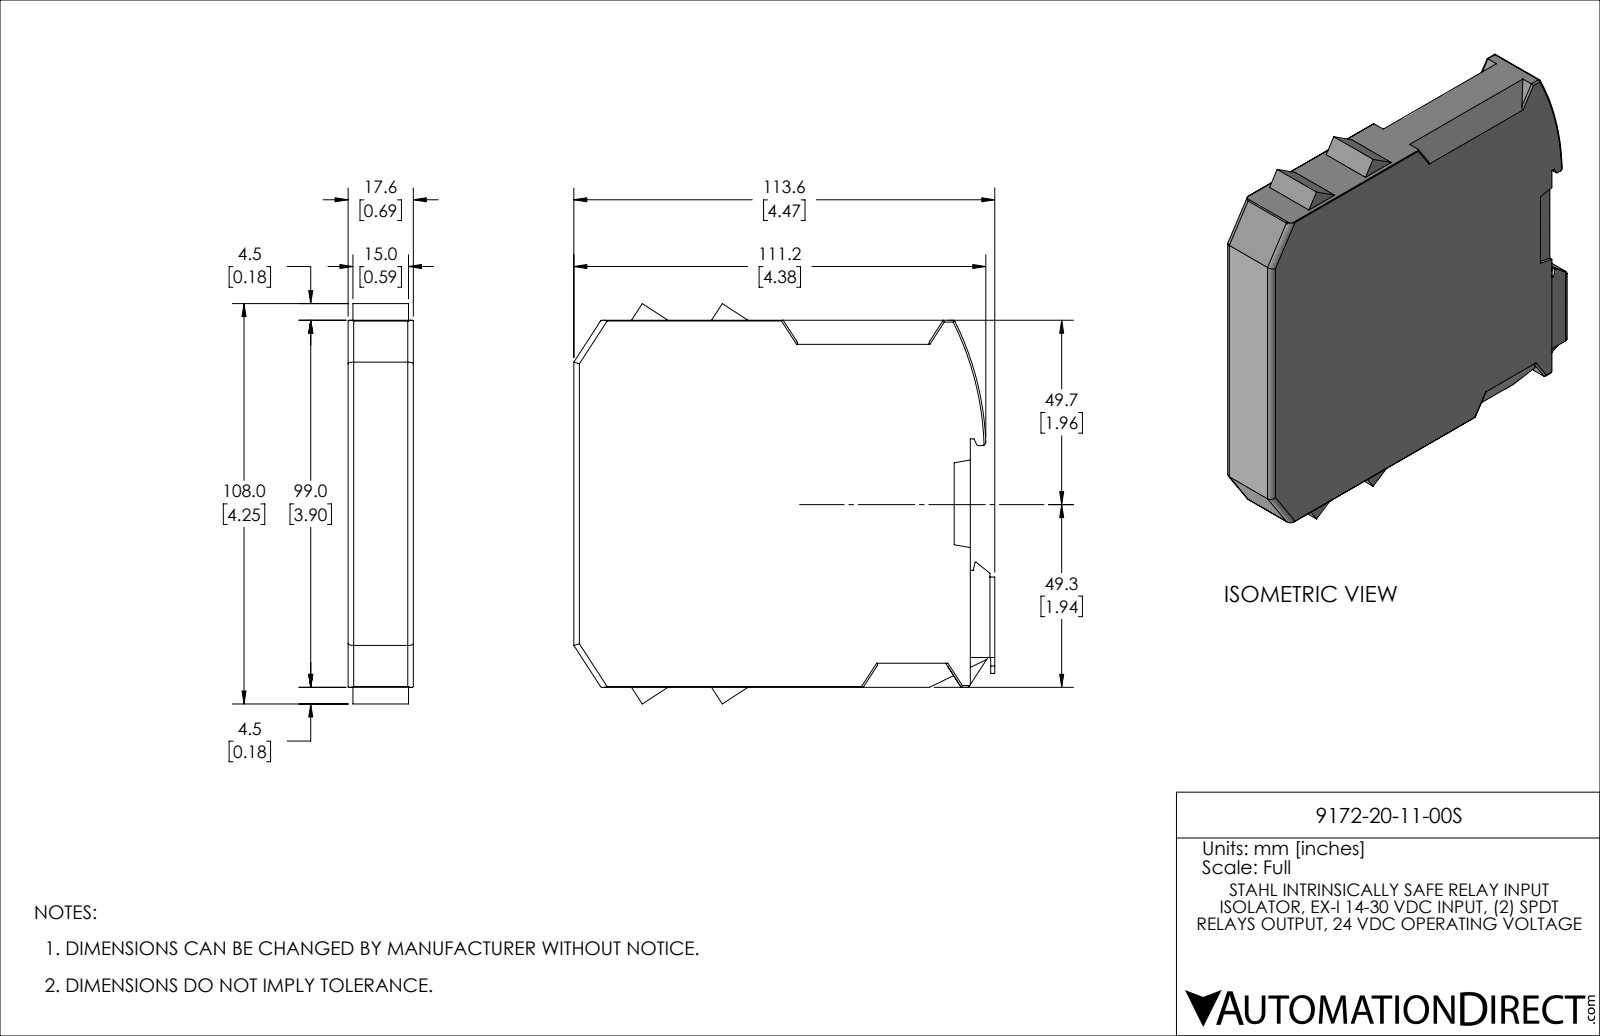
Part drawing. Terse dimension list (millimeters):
name: 9172-20-11-00S
written by: SolidWorks 2021 (AUTOMOTIVE_DESIGN)
unit: mm
bodies: 1 solid, 175 faces (121 planar, 52 cylindrical, 2 other)
size: 113.6 × 108 × 17.6
volume: 187 100 mm³; area: 29 500 mm²
rounds: 17× R0.5, 6× R1.5, 4× R0.2, 4× R0.7, 2× R1.3, 2× R2, 1× R1, 1× R80
face distances: 17.6, 99, 107, 1.1, 6.6, 113.6, 5.5, 112.5, 58.2, 1.5
